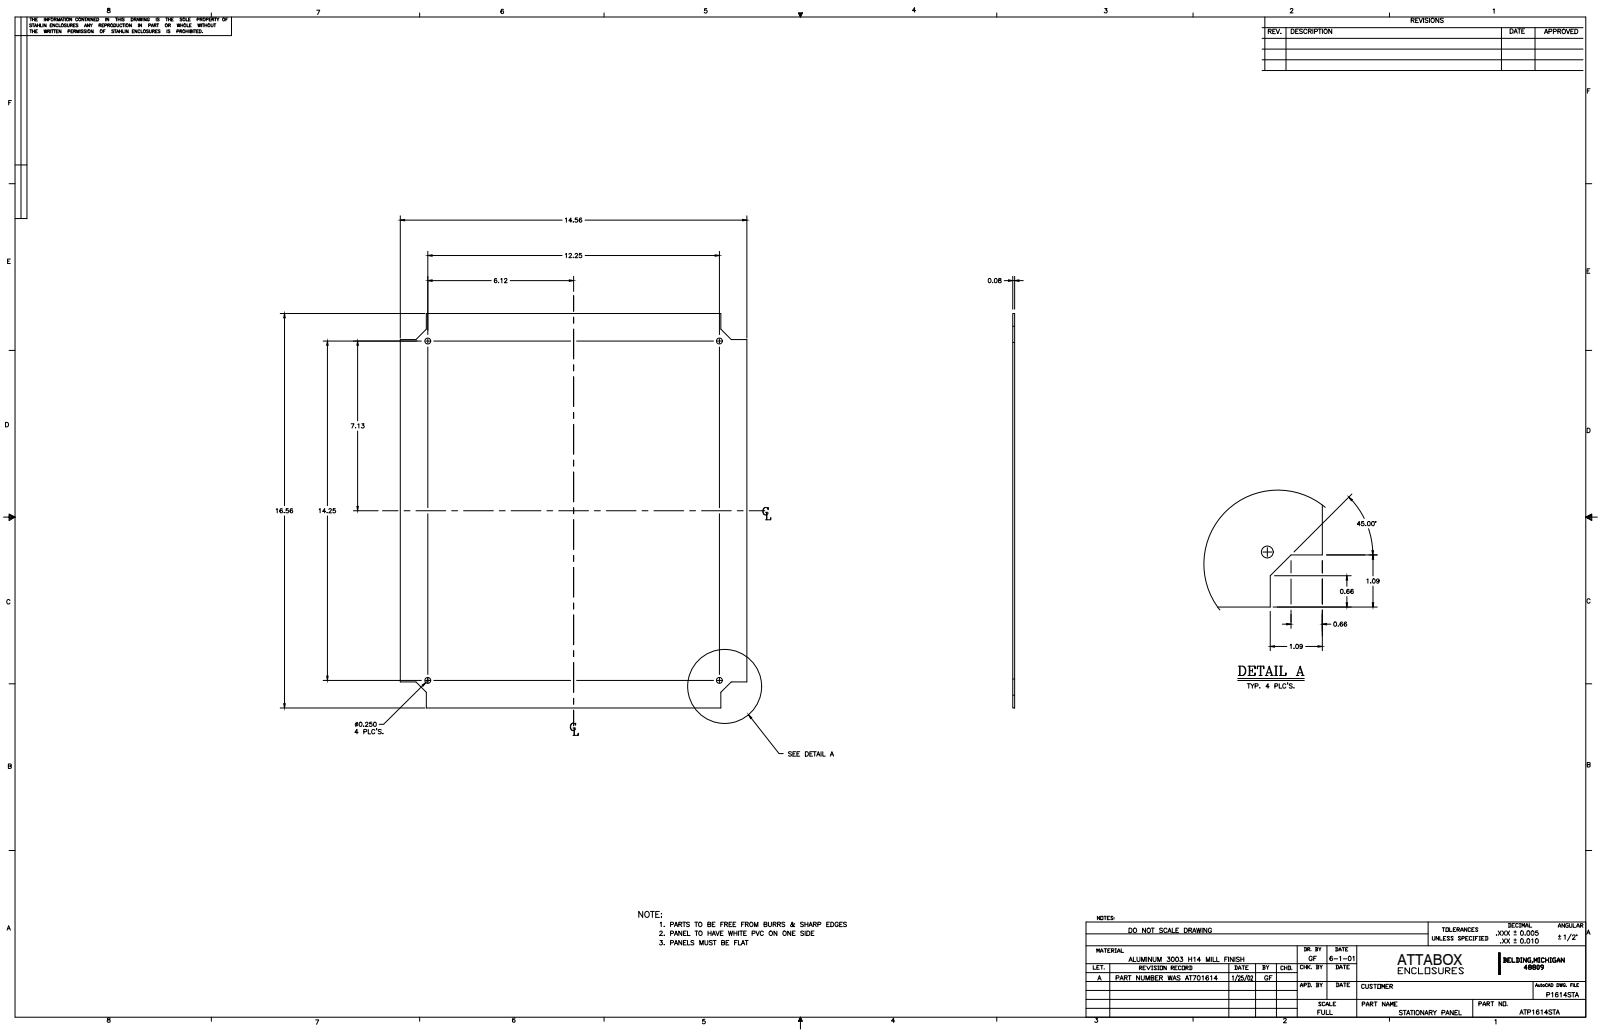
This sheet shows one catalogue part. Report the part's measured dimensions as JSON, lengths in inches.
{"part_name": "P1614STAL", "step_written_by": "Autodesk Inventor 11 (AUTOMOTIVE_DESIGN)", "units": "inches", "bodies": {"solids": 1, "faces": 22, "planar": 18, "cylindrical": 4, "other": 0}, "overall_size": [16.563, 14.563, 0.08], "volume_in3": 18.93, "surface_area_in2": 478.3, "round_holes": [[0.25, 4]], "face_to_face_distances": [0.08, 14.562, 16.562, 1.094, 13.468, 15.468, 12.374, 14.374, 19.529], "hole_center_spacings": [12.25, 14.25, 18.792]}
